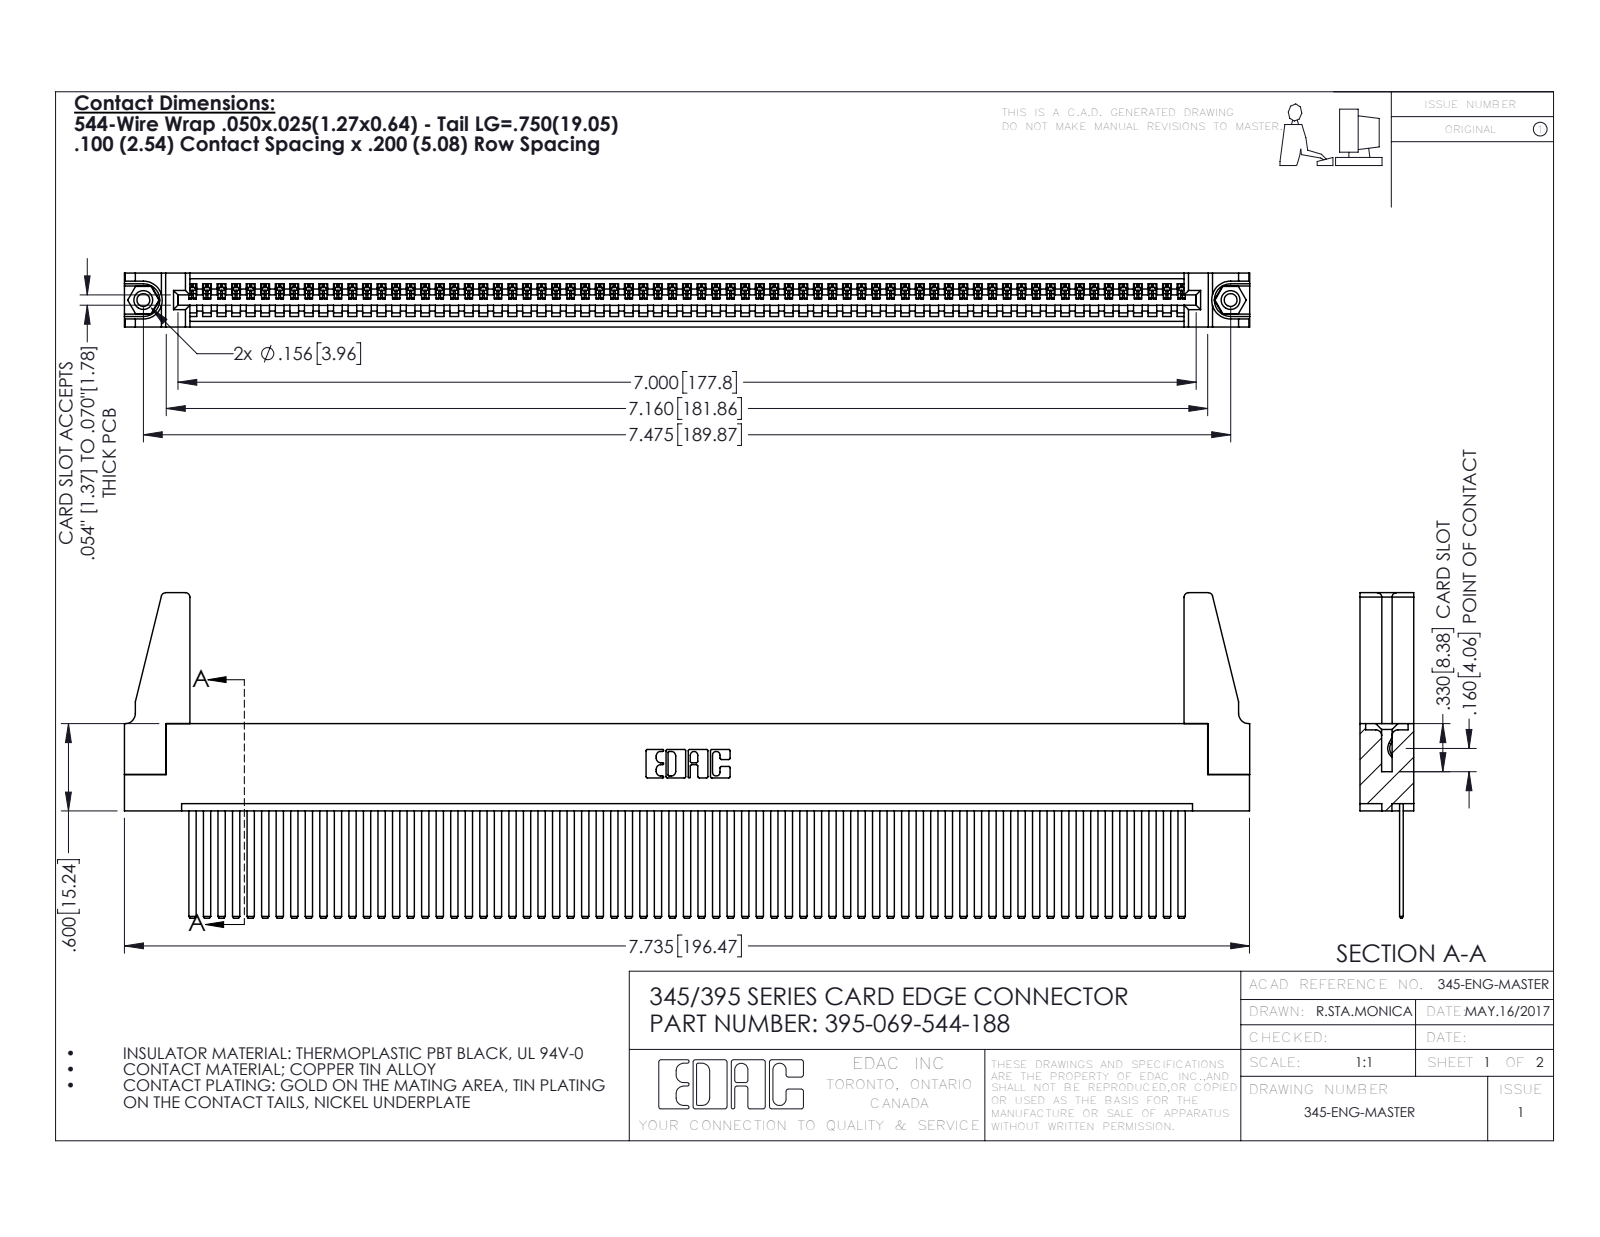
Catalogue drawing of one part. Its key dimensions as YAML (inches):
part_name: "345 Part_Flush Mounting Lugs - 0.156 Dia-TH; 345-250-001_345-250-001-102; 345-220-078_345-220-088; 395-069-544-188 (+1 more)"
step_written_by: "SolidWorks 2016 (CONFIG_CONTROL_DESIGN)"
units: inches
bodies: {solids: 74, faces: 3838, planar: 2636, cylindrical: 1186, other: 16}
overall_size: [7.736, 2.237, 0.37]
volume: 1.4
surface_area: 49.68
round_holes:
  - {diameter: 0.089, count: 2}
  - {diameter: 0.125, count: 2}
  - {diameter: 0.156, count: 2}
  - {diameter: 0.064, count: 1}
round_bosses_or_shafts:
  - {diameter: 0.155, count: 2}
partial_cylinders:
  - {radius: 0.006, count: 138}
  - {radius: 0.01, count: 22}
  - {radius: 0.03, count: 8}
  - {radius: 0.007, count: 6}
  - {radius: 0.031, count: 6}
  - {radius: 0.026, count: 3}
  - {radius: 0.031, count: 2}
  - {radius: 0.04, count: 2}
face_to_face_distances: [0.072, 0.298, 0.098, 0.272, 0.025, 0.37, 0.2, 0.225, 0.149, 0.072]
hole_center_spacings: [0.27, 7.239, 7.475]
